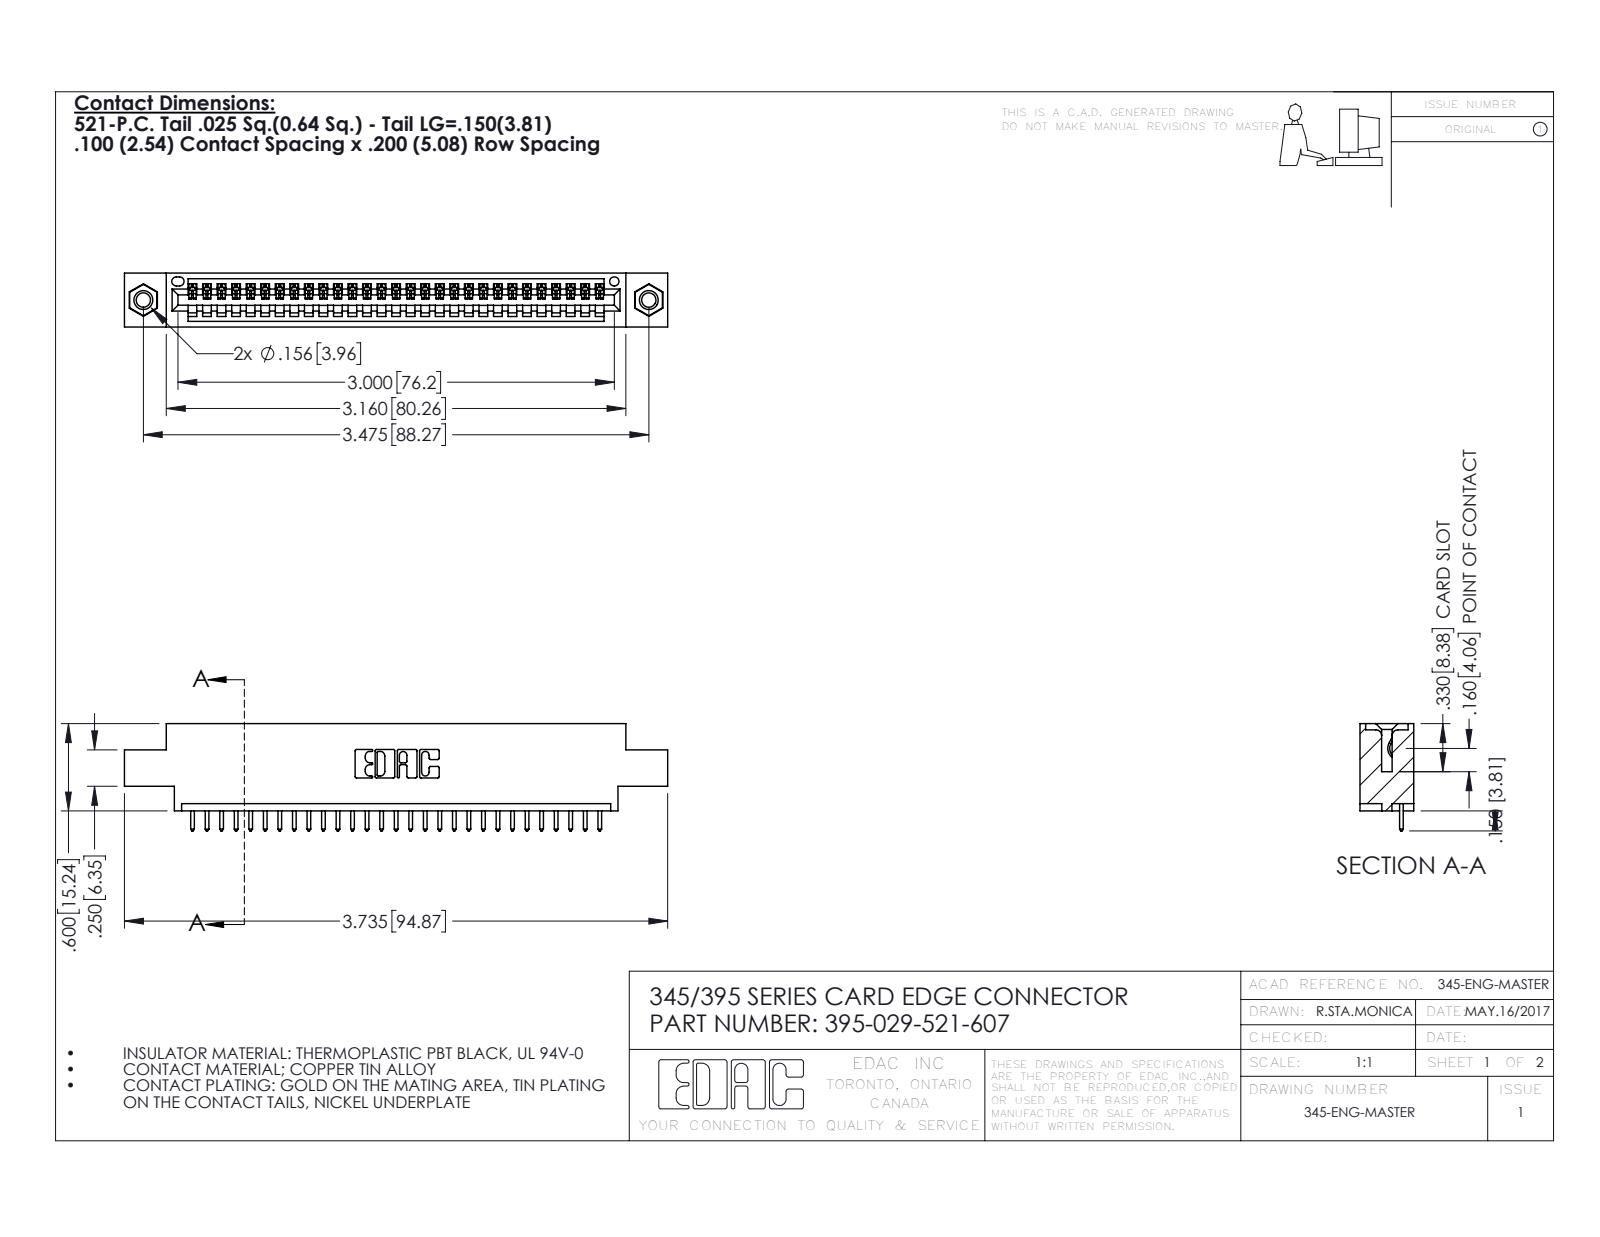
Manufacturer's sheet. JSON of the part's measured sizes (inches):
{"part_name": "345-250-001_345-250-005-103; 345 Part_0.170 Offset - 0.156 Dia-TI; 345-292-001_345-293-121; 395-029-521-607", "step_written_by": "SolidWorks 2016 (CONFIG_CONTROL_DESIGN)", "units": "inches", "bodies": {"solids": 32, "faces": 1872, "planar": 1276, "cylindrical": 580, "other": 16}, "overall_size": [3.735, 0.737, 0.37], "volume_in3": 0.531, "surface_area_in2": 17.38, "round_holes": [[0.098, 2], [0.125, 2], [0.156, 2], [0.064, 1]], "round_bosses_or_shafts": [[0.155, 2]], "partial_cylinders_radius": [[0.006, 58], [0.01, 58], [0.01, 22], [0.007, 6], [0.031, 6], [0.026, 3], [0.031, 2], [0.04, 2]], "face_to_face_distances": [0.072, 0.298, 0.37, 0.2, 0.098, 0.272, 0.025, 0.225, 0.175, 0.149], "hole_center_spacings": [0.27, 3.24, 3.475]}
